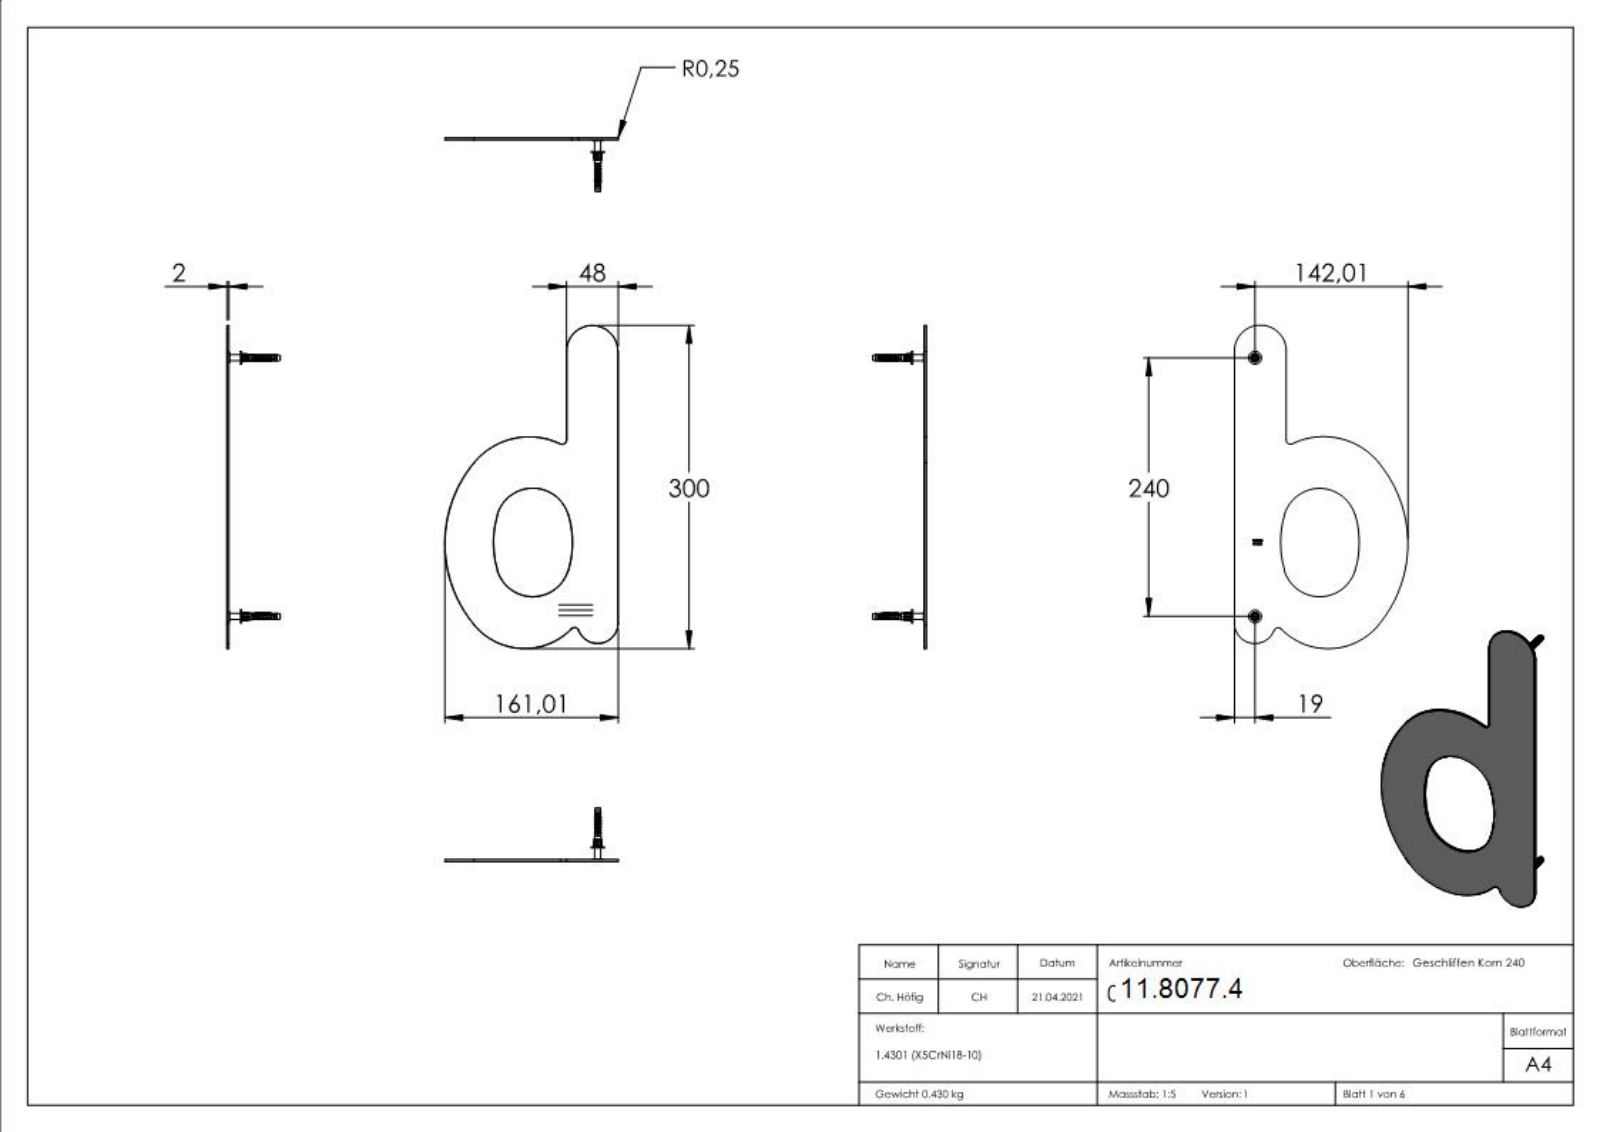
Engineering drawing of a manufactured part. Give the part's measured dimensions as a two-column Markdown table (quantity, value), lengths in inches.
| quantity | value |
| --- | --- |
| part name | 041-HN-D; 041-HN-X Teil4; 041-HN-X Teil3; 041-HN-X Teil2 (+5 more) |
| STEP written by | SolidWorks 2018 (CONFIG_CONTROL_DESIGN) |
| units | inches |
| bodies | 7 solids, 1559 faces (365 planar, 390 cylindrical, 804 other) |
| overall size | 393.701 × 205.411 × 181.413 |
| volume | 3.38 in³ |
| surface area | 91.82 in² |
| round holes (diameter × count) | 0.13 × 2, 0.169 × 2 |
| round bosses / shafts (diameter × count) | 0.472 × 2, 0.354 × 2, 0.315 × 2, 0.236 × 2, 0.228 × 2, 0.22 × 2, 0.181 × 2, 0.157 × 2 |
| partial cylindrical surfaces (radius × count) | 0.004 × 22, 0.01 × 2, 0.138 × 2, 0.157 × 2, 1.348 × 2, 0.748 × 1, 0.945 × 1, 2.402 × 1 |
| main face-to-face distances | 0.079, 0.457, 0.535, 0.043, 0.413, 0.492, 1.89, 0.039, 0.02, 0.098 |
| hole center spacings | 9.449 |
